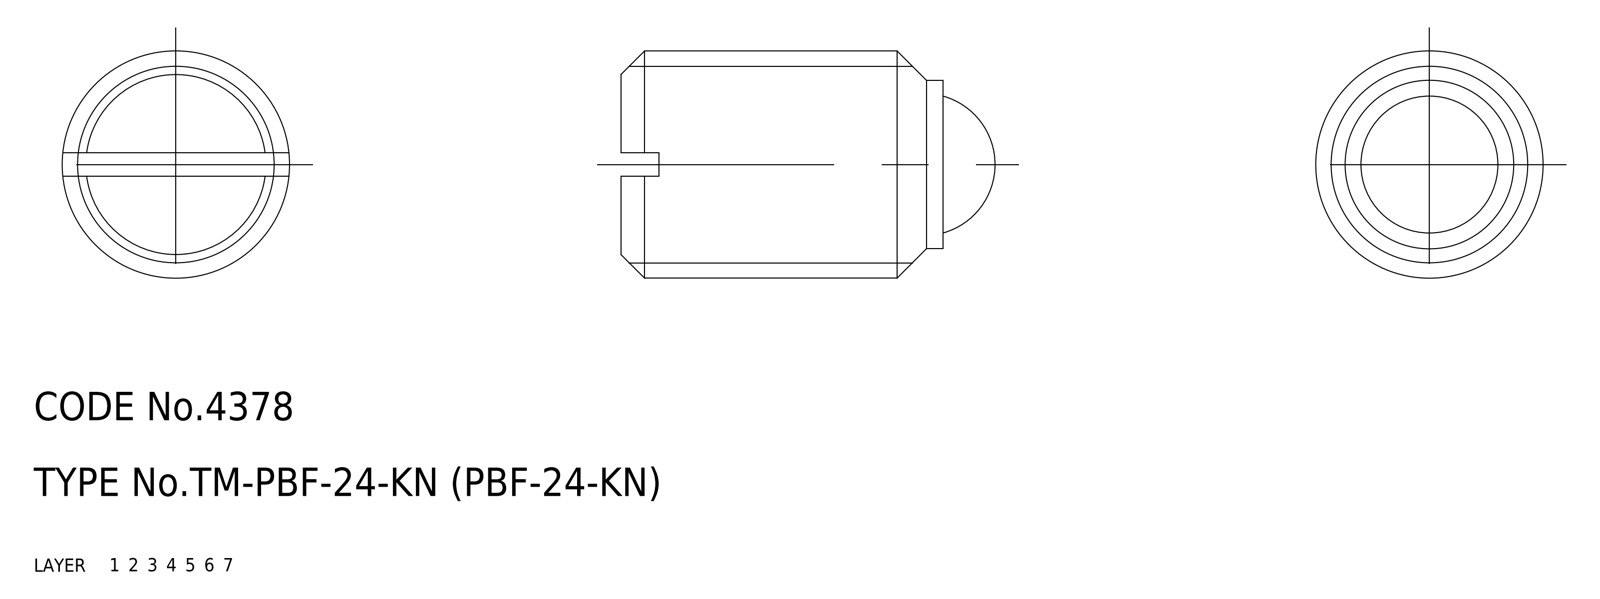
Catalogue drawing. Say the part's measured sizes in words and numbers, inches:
The part is named "ball; PBF_24_KN_14289_36". Its 3-D file was written by "CADfix (AUTOMOTIVE_DESIGN)". It is 2 solids with 19 faces: 0 planar, 0 cylindrical and 19 other. Overall it measures 1.555 by 0.945 by 0.945 inches. Its volume is 0.796 cubic inches and its surface area 7.5 square inches.
